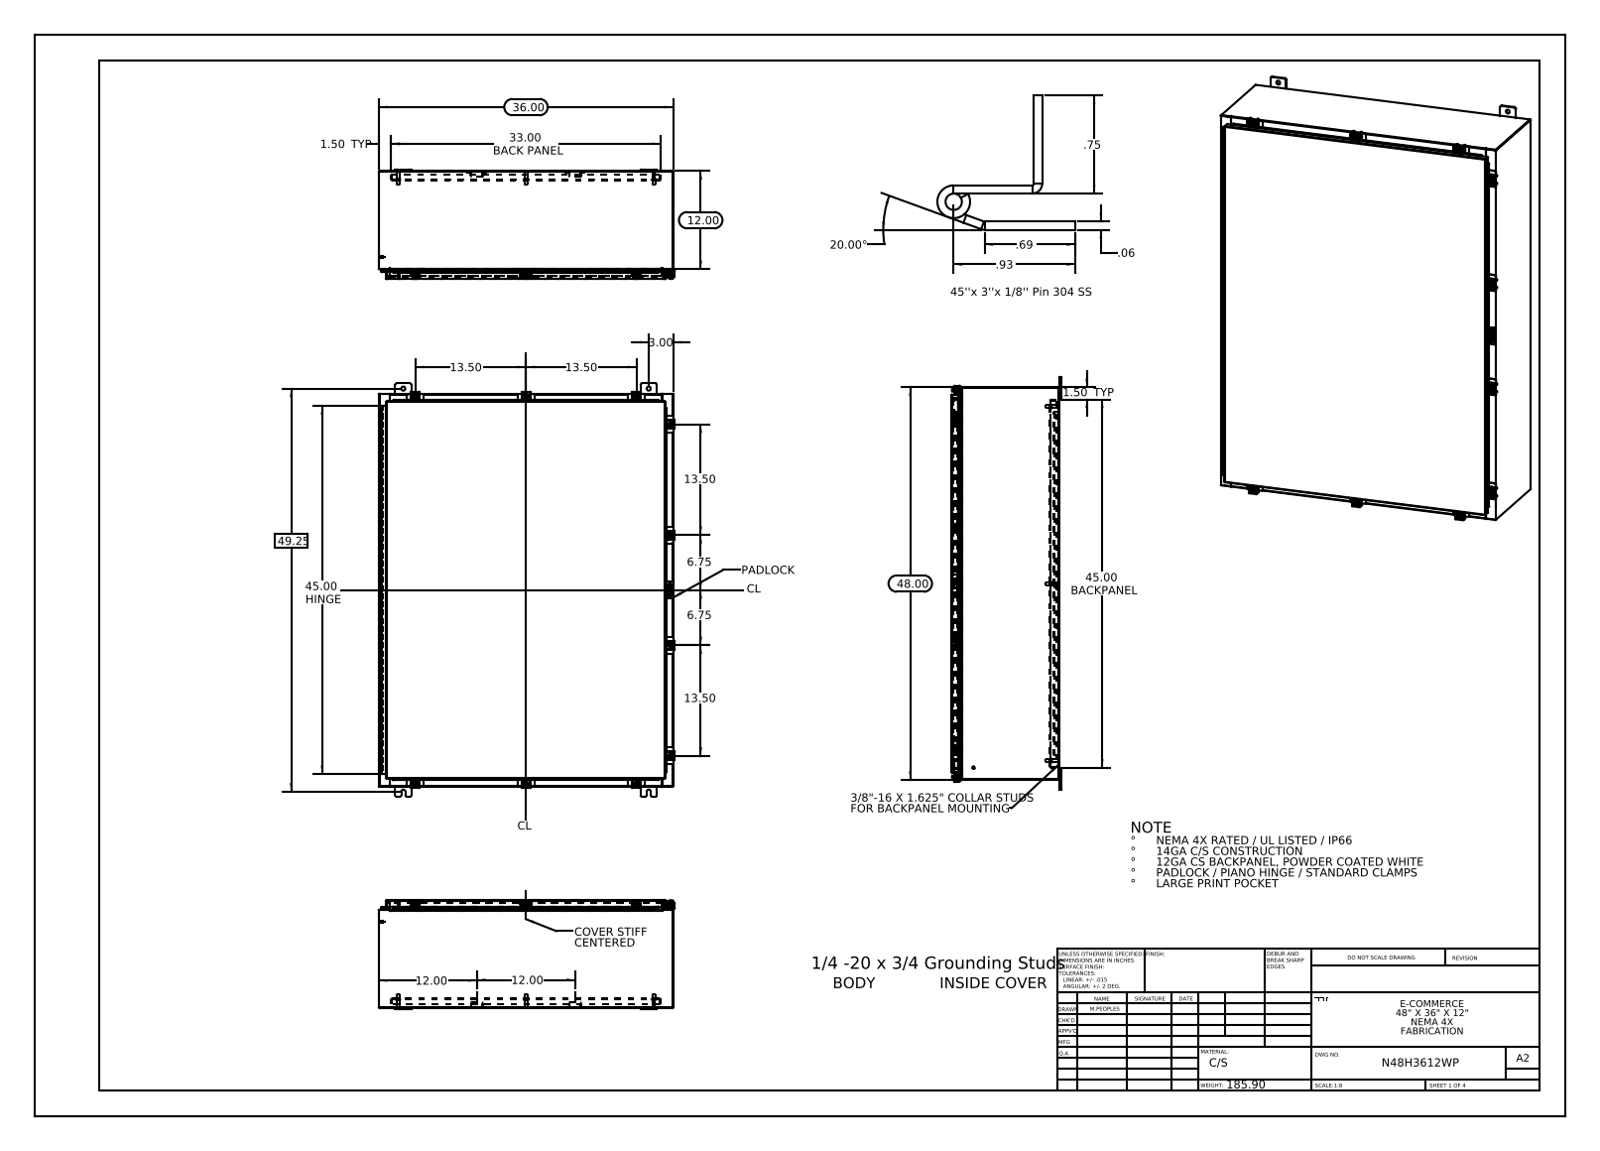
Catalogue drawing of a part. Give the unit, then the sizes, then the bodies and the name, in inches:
Units: inches
Overall size (bounding box): 50.5 × 36.211 × 13.389
Round holes (diameter × count): ⌀0.5 ×12, ⌀0.213 ×10, ⌀0.26 ×10, ⌀0.25 ×6, ⌀0.125 ×2
Round bosses / shafts (diameter × count): ⌀0.25 ×11, ⌀0.5 ×10, ⌀0.399 ×10, ⌀0.625 ×8, ⌀0.375 ×8, ⌀0.33 ×8, ⌀0.157 ×6, ⌀0.14 ×6
Partial cylindrical surfaces — rounded edges, fillets, slot ends (radius × count): R0.06 ×46, R0.013 ×39, R0.088 ×33, R0.19 ×24, R0.12 ×20, R0.141 ×20, R0.05 ×15, R0.08 ×14
Main face-to-face distances: 0.075, 13.126, 13.051, 0.104, 13.201, 1, 12.126, 1.075, 12.051, 1.179
Hole centre spacings: 13.5, 13.663, 20, 20.123, 21.625, 23.82, 27, 38.003
Volume: 650.9 in³ · Surface area: 16 262 in²
Bodies: 82 solids, 3115 faces (1586 planar, 1301 cylindrical, 228 other)
Part name (STEP PRODUCT): N48H3612SSWP Top; N48H3612SSWP Enclosure Stiffener; 10_30 CD Stud; N48H3612SSWP Padlock Staple (+8 more)
STEP written by: SolidWorks 2013 (CONFIG_CONTROL_DESIGN)
